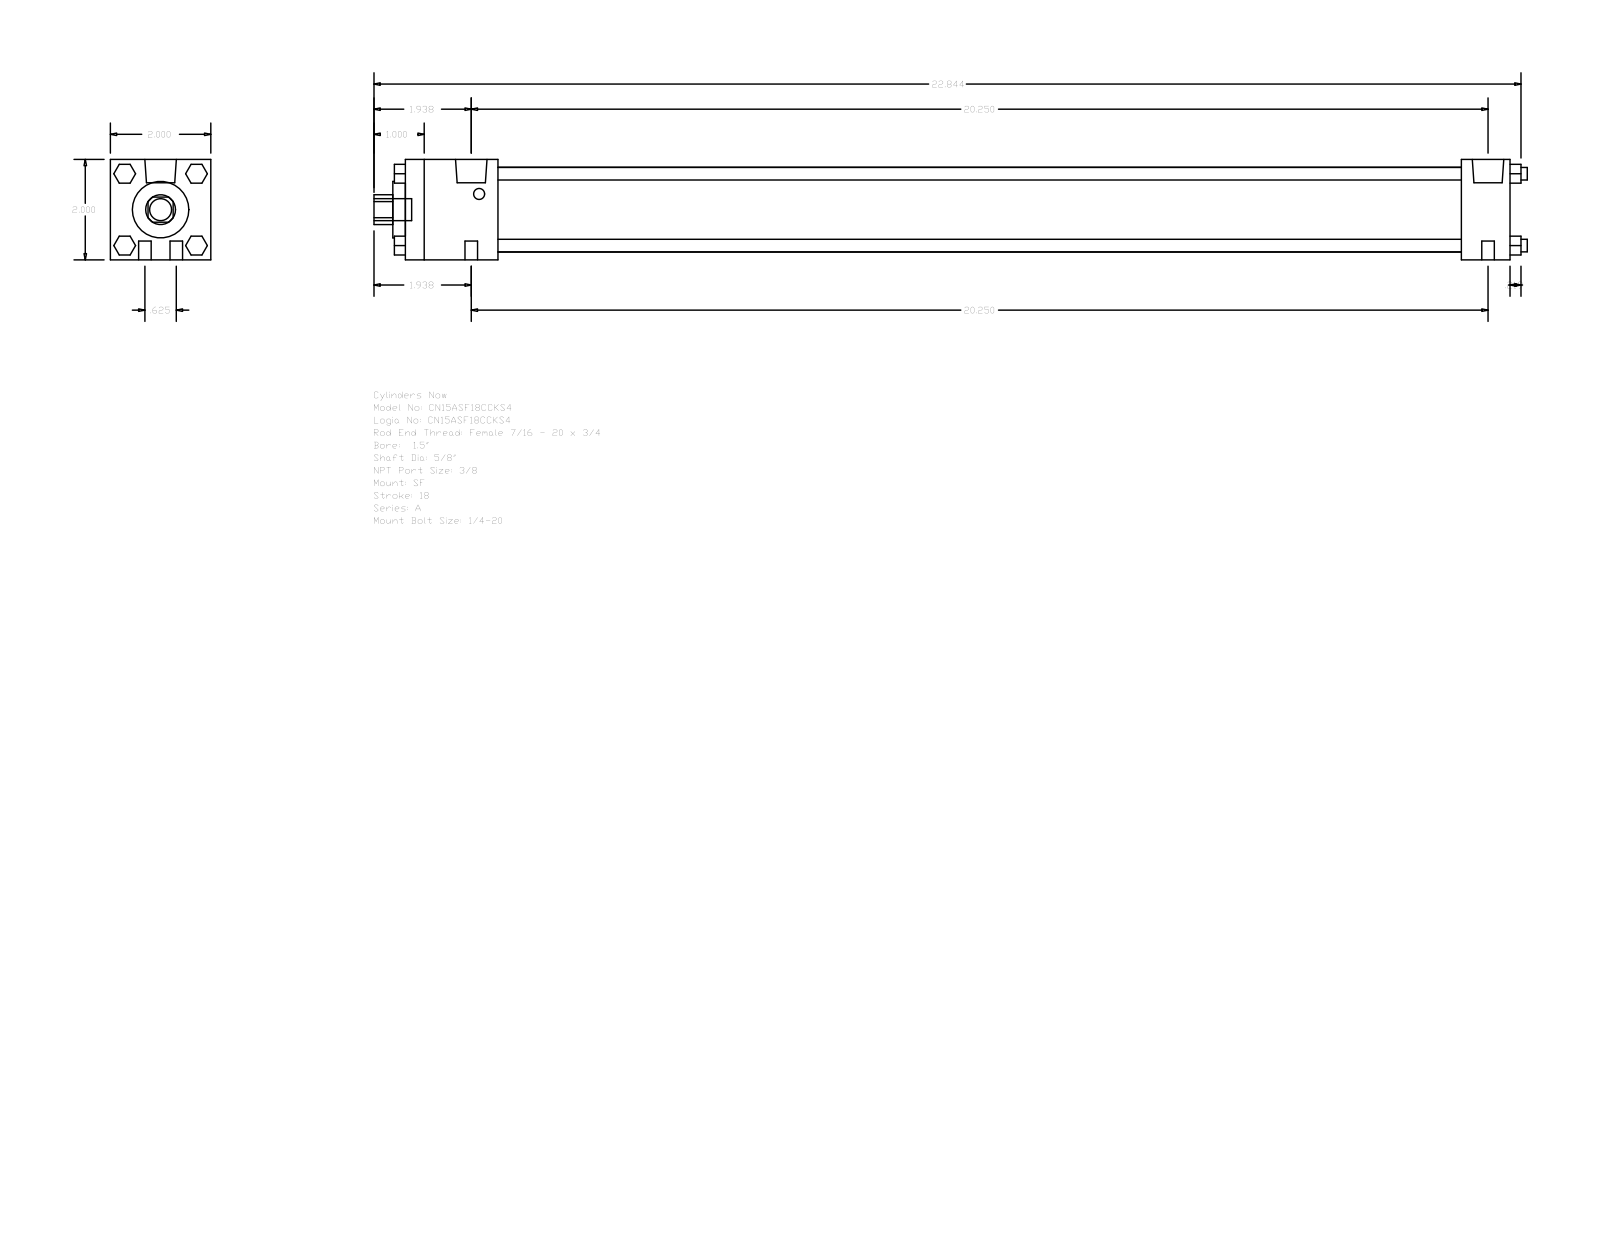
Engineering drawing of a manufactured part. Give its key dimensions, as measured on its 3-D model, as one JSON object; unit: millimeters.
{"part_name": "A_SF__0150_0.625", "step_written_by": "GSSL Pune (CONFIG_CONTROL_DESIGN)", "units": "millimeters", "bodies": {"solids": 0, "faces": 124, "planar": 94, "cylindrical": 30, "other": 0}, "overall_size": [583.41, 50.8, 50.8], "round_holes": [[15.88, 1], [28.57, 1], [42.93, 1]], "round_bosses_or_shafts": [[6.35, 8], [15.93, 2], [5.56, 2], [11.11, 1]], "partial_cylinders_radius": [[7.54, 1]], "face_to_face_distances": [50.8, 558.79, 46.83, 534.19, 487.36, 511.96, 24.6, 9.52, 6.35, 53.18]}
